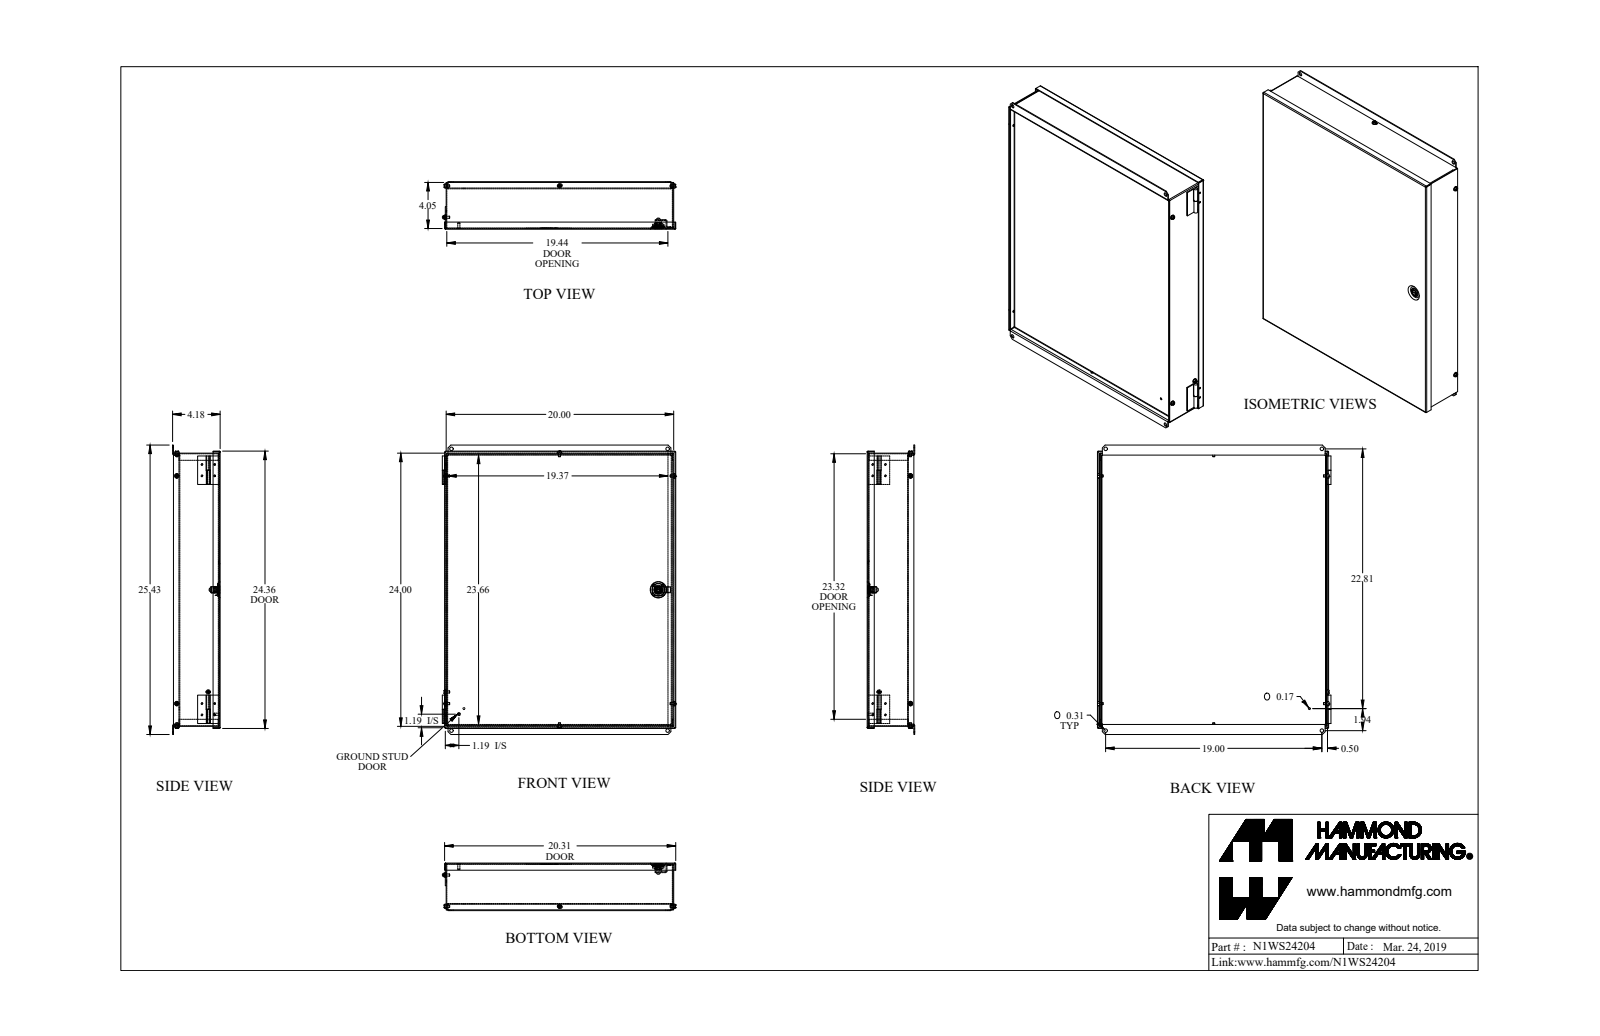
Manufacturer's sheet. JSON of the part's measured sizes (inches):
{"part_name": "N1WS24204", "step_written_by": "SolidWorks 2018 (AUTOMOTIVE_DESIGN)", "units": "inches", "bodies": {"solids": 17, "faces": 607, "planar": 328, "cylindrical": 214, "other": 65}, "overall_size": [25.425, 20.519, 4.179], "volume_in3": 92.34, "surface_area_in2": 2964, "round_holes": [[0.14, 8], [0.17, 5], [0.312, 4], [0.187, 1], [0.319, 1], [0.476, 1]], "round_bosses_or_shafts": [[0.128, 8], [0.19, 4], [0.375, 3], [0.787, 1], [0.547, 1], [0.472, 1], [0.469, 1], [0.375, 1]], "partial_cylinders_radius": [[0.029, 9], [0.086, 9], [0.036, 8], [0.108, 6], [0.109, 6], [0.012, 4], [0.1, 4], [0.079, 2]], "face_to_face_distances": [0.072, 0.057, 3.564, 3.621, 3.492, 3.549, 0.057, 19.943, 23.943, 19.886], "hole_center_spacings": [1, 1.119, 1.501, 21, 21.03, 20, 2.195, 2.412]}
